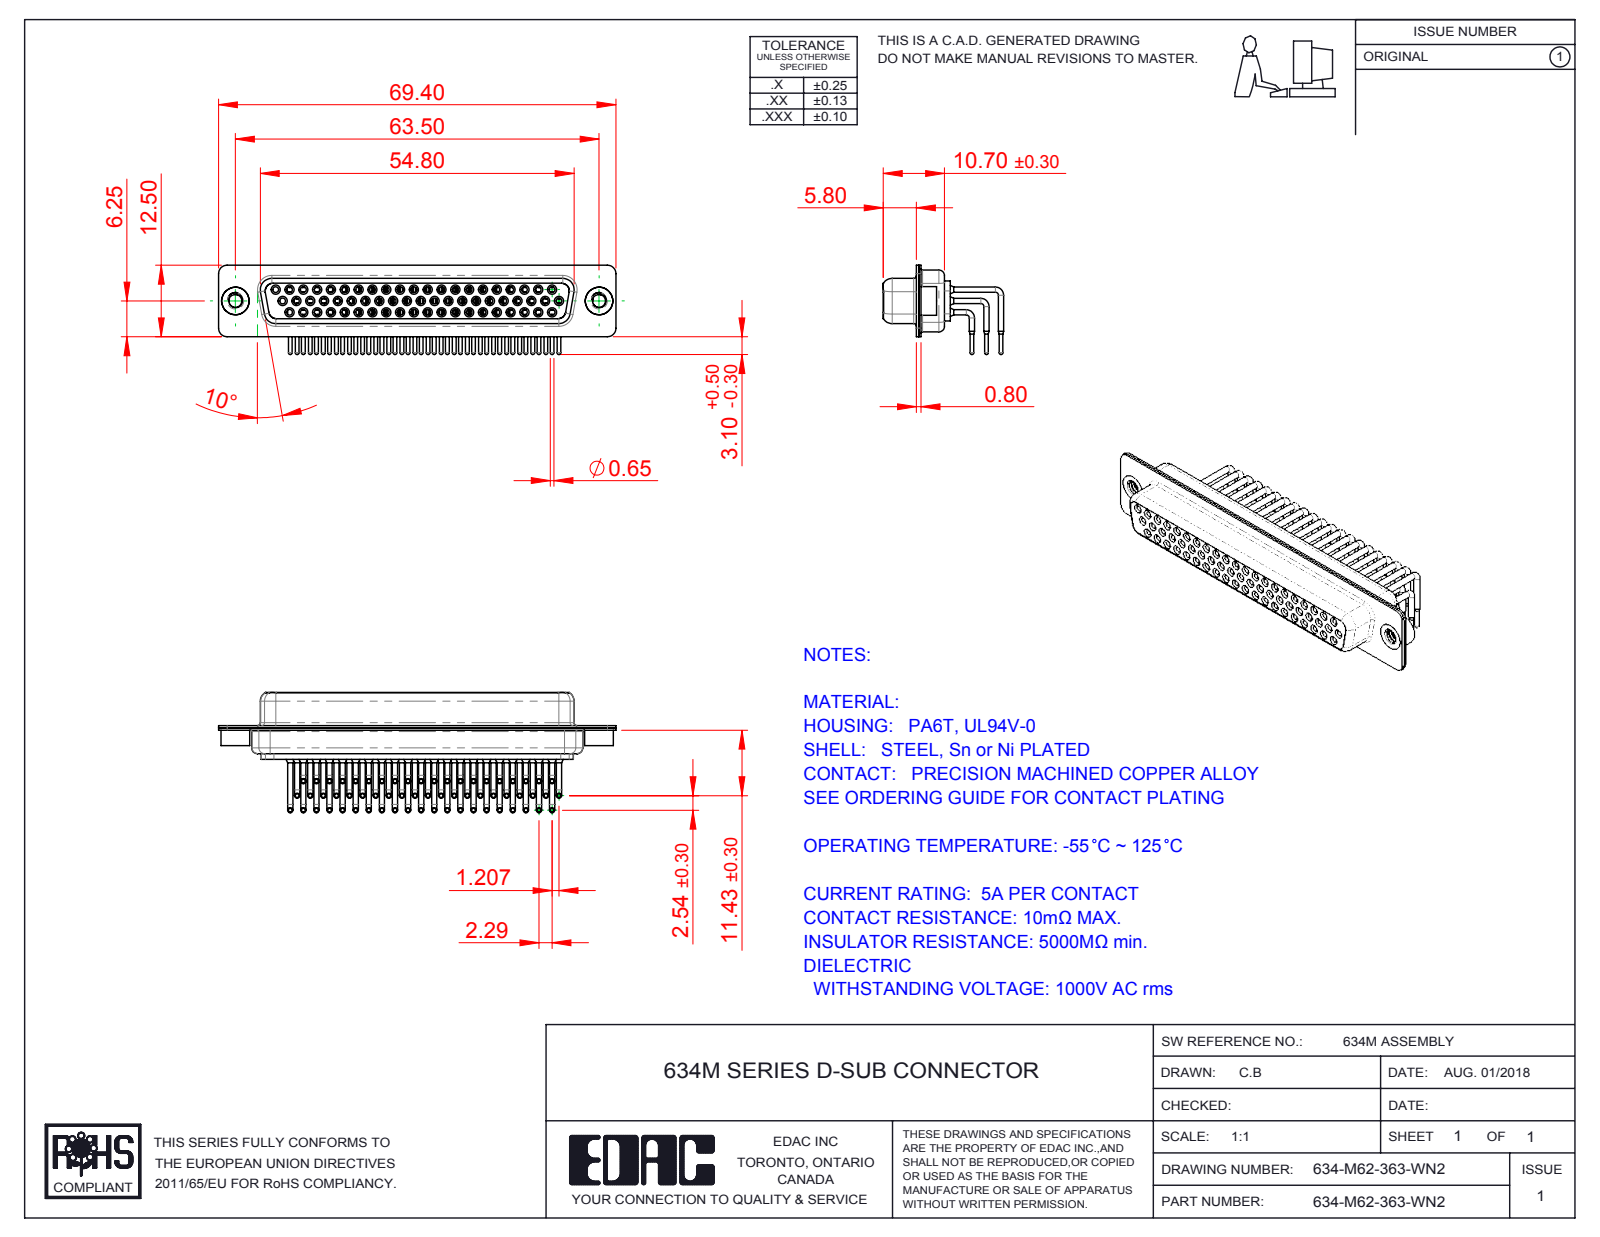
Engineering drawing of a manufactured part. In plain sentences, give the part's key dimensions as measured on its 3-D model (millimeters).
The part is named "634M Contact Row 1; 634M Shell Front_62 Contacts; 634M Contact Row 3; 634M Housing_62 Contacts (+4 more)". Its 3-D file was written by "SolidWorks 2016 (CONFIG_CONTROL_DESIGN)". It is 67 solids with 3565 faces: 997 planar, 1563 cylindrical and 1005 other. Overall it measures 69.4 by 21.02 by 15.6 millimeters. Its volume is 5 405 cubic millimeters and its surface area 17 868 square millimeters. Round holes: 62 of diameter 1, 62 of diameter 1.1, 62 of diameter 1.7, 62 of diameter 1.8, 62 of diameter 2, 2 of diameter 2.26, 2 of diameter 4, 2 of diameter 4.8. Round bosses or shafts: 124 of diameter 0.9, 62 of diameter 1.6, 62 of diameter 1.5, 62 of diameter 0.65, 56 of diameter 2, 2 of diameter 5, 2 of diameter 4.9. Partial cylindrical surfaces (rounded edges, fillets, slot ends): 16 of radius 1.5, 12 of radius 2, 8 of radius 1.35, 8 of radius 1.6, 4 of radius 0.25, 4 of radius 0.5, 4 of radius 0.6, 4 of radius 0.65. The main face-to-face distances are 0.4, 1.45, 8.95, 1.9, 8.5, 2.3, 6.2, 0.45, 7.05, 0.85. The hole center spacings are 7.24, 2.32, 2.41, 9.65, 4.13, 4.83, 16.89, 14.48.
